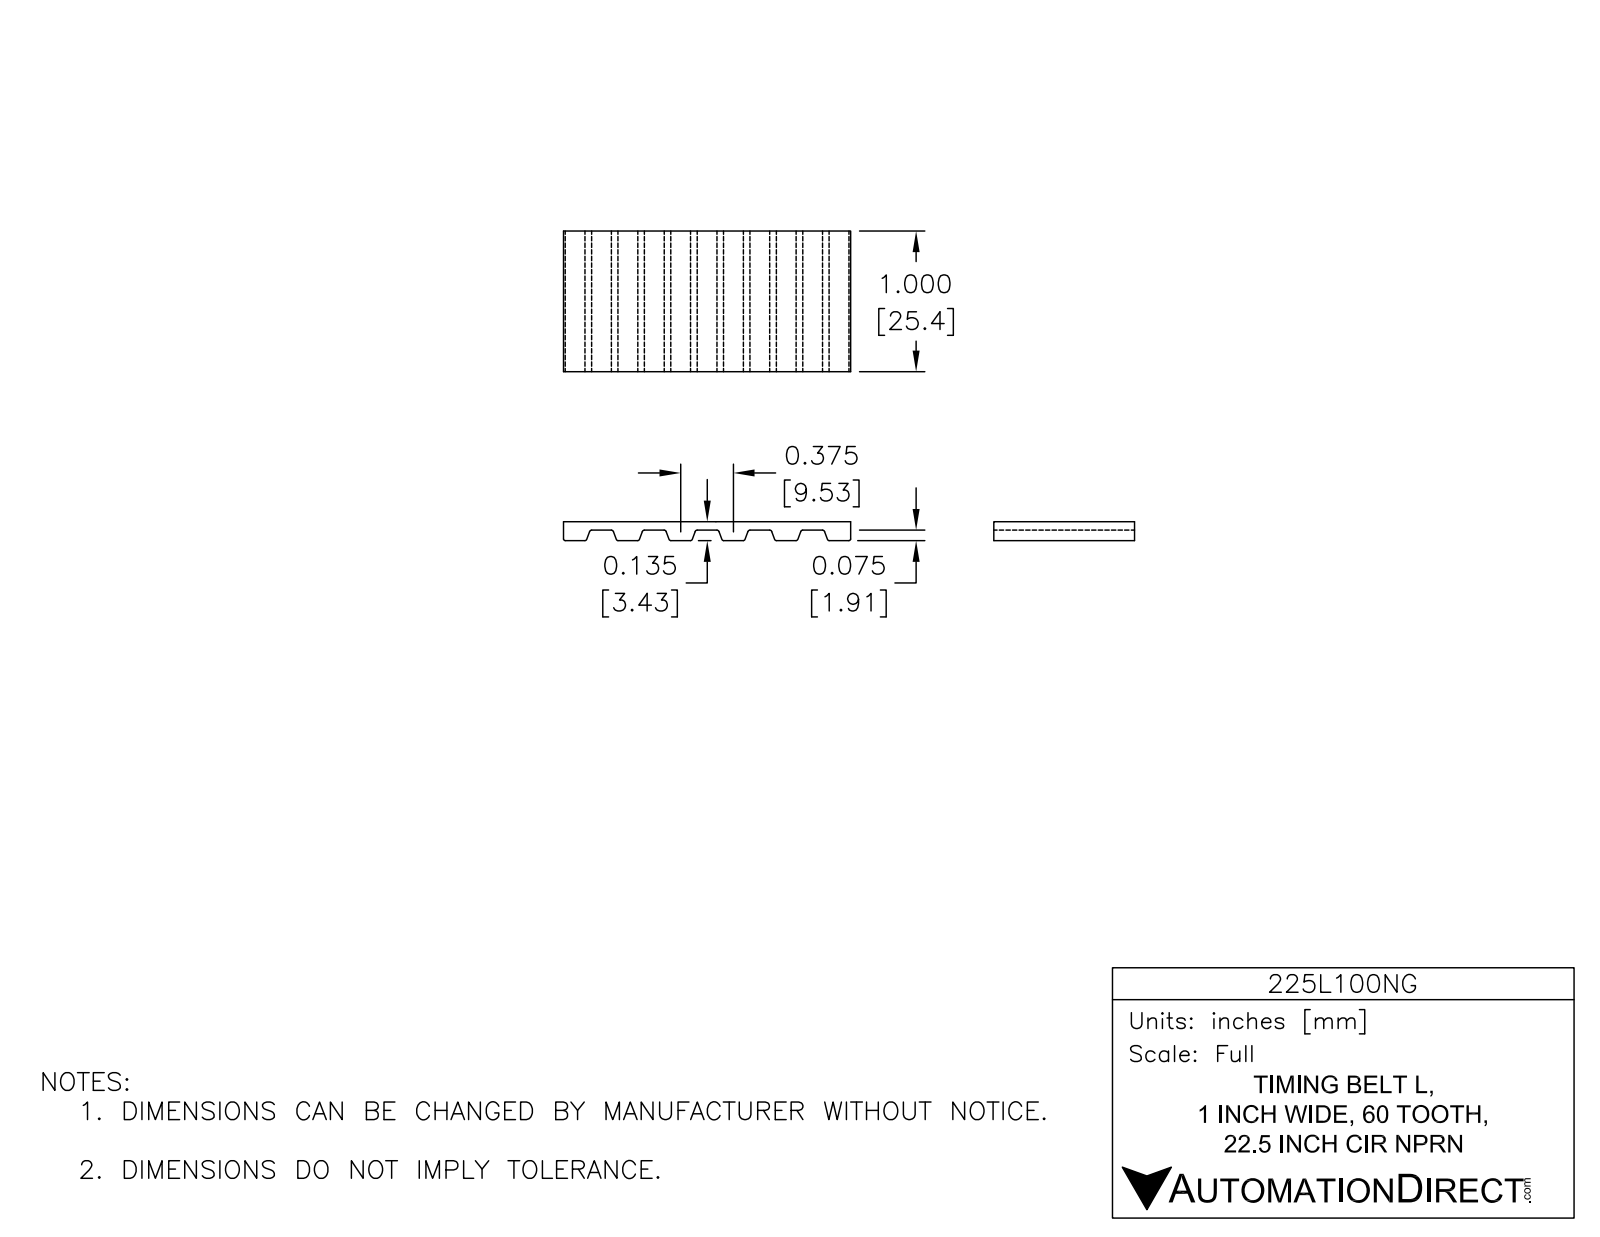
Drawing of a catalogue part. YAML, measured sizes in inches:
part_name: "225L100NG"
step_written_by: "SolidWorks 2014 (AUTOMOTIVE_DESIGN)"
units: inches
bodies: {solids: 1, faces: 494, planar: 216, cylindrical: 278, other: 0}
overall_size: [9.538, 3, 1]
volume: 2.027
surface_area: 53.98
partial_cylinders:
  - {radius: 0.02, count: 236}
  - {radius: 1.435, count: 2}
  - {radius: 1.5, count: 2}
face_to_face_distances: [0.065, 2.935, 3, 2.87, 0.14, 2.86, 0.075, 2.795, 1, 2.72]
